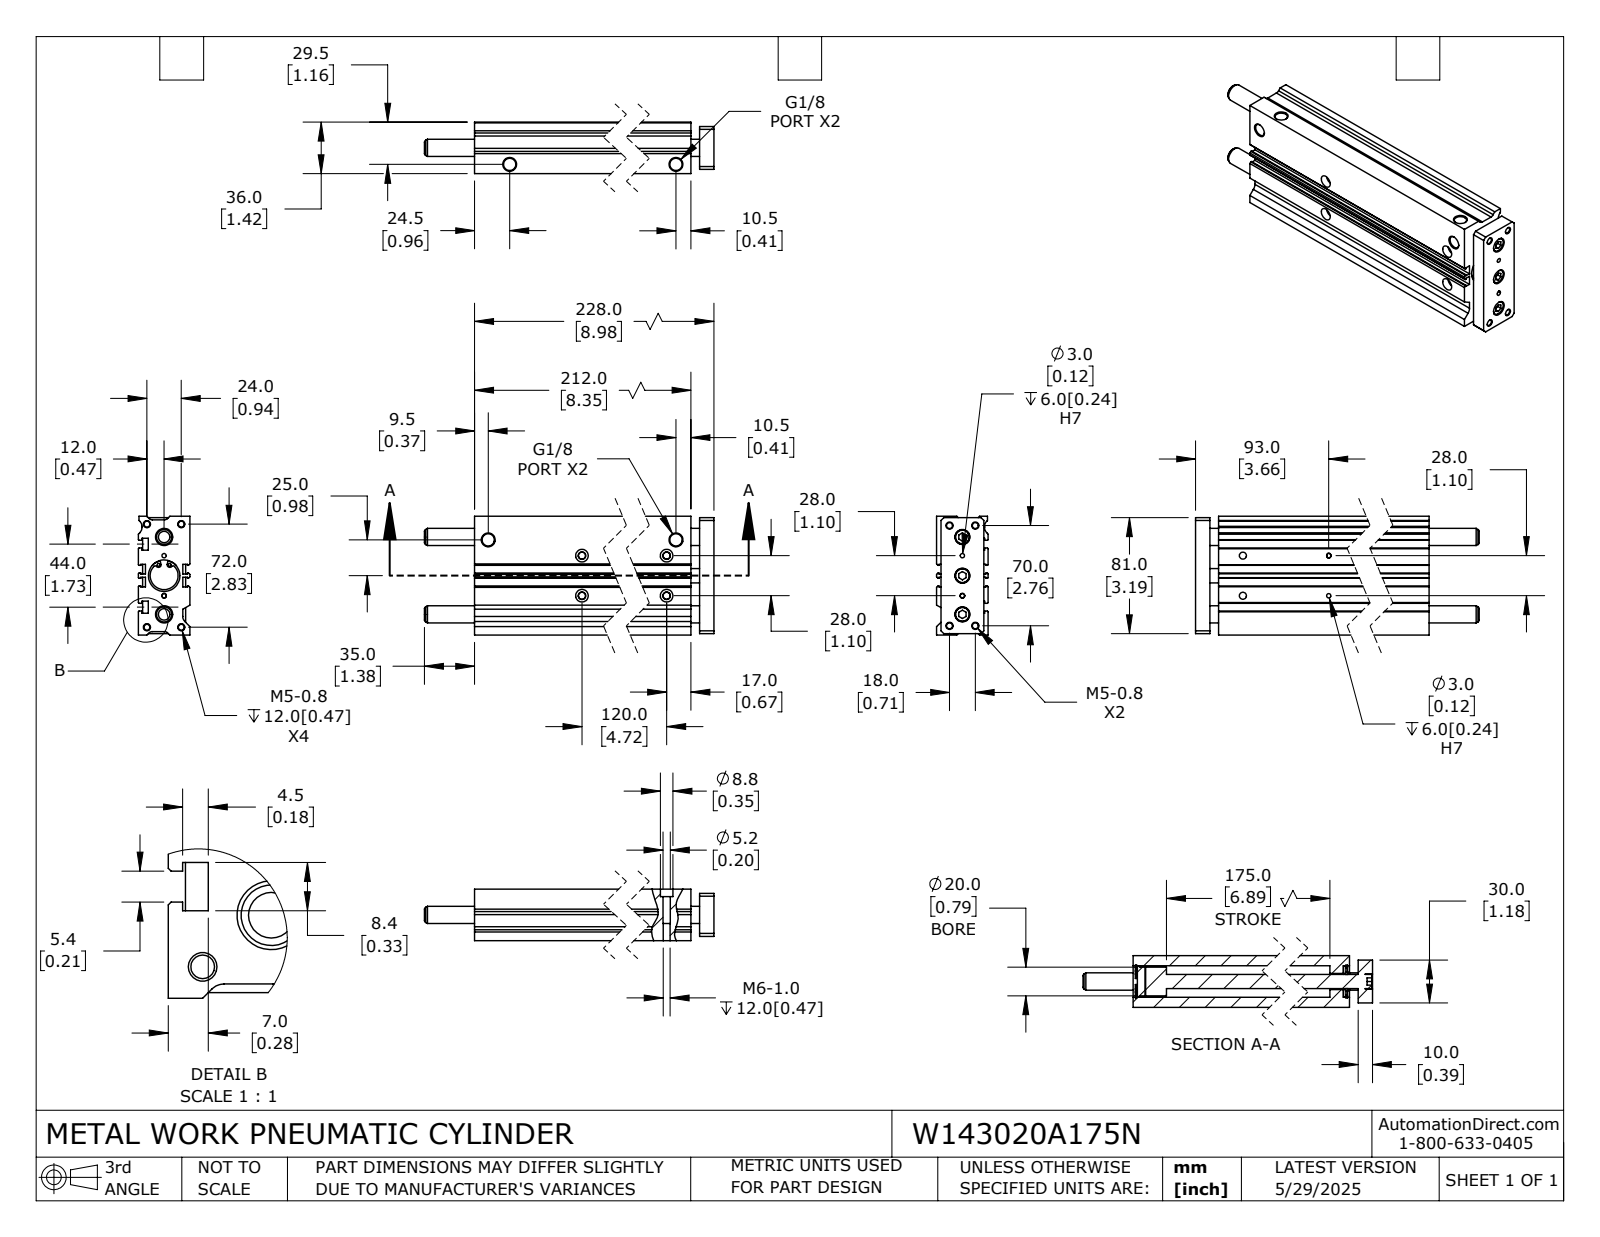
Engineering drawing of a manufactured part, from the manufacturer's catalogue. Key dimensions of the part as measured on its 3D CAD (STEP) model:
Part name (STEP PRODUCT): W143020A175N; W143020A175N_BODY; W143020A175N_ROD
STEP written by: SolidWorks 2024 (CONFIG_CONTROL_DESIGN)
Units: inches
Bodies: 6 solids, 357 faces (174 planar, 145 cylindrical, 38 other)
Overall size (bounding box): 10.354 × 3.268 × 1.417
Volume: 32.06 in³ · Surface area: 228.9 in²
Round holes (diameter × count): ⌀0.163 ×8, ⌀0.079 ×4, ⌀0.118 ×4, ⌀0.205 ×4, ⌀0.337 ×4, ⌀0.346 ×4, ⌀0.413 ×3, ⌀0.194 ×2, ⌀0.194 ×2, ⌀0.472 ×2, ⌀0.449 ×1, ⌀0.767 ×1
Round bosses / shafts (diameter × count): ⌀0.394 ×3, ⌀0.906 ×2, ⌀0.787 ×1, ⌀0.512 ×1
Partial cylindrical surfaces — rounded edges, fillets, slot ends (radius × count): R0.053 ×4, R0.059 ×4, R0.071 ×4, R0.118 ×4, R0.197 ×3
Main face-to-face distances: 1.417, 0.098, 0.197, 1.22, 0.079, 3.268, 1.024, 0.276, 3.169, 0.945
Hole centre spacings: 0.124, 0.296, 0.336, 0.474, 0.591, 0.78, 0.828, 0.864
